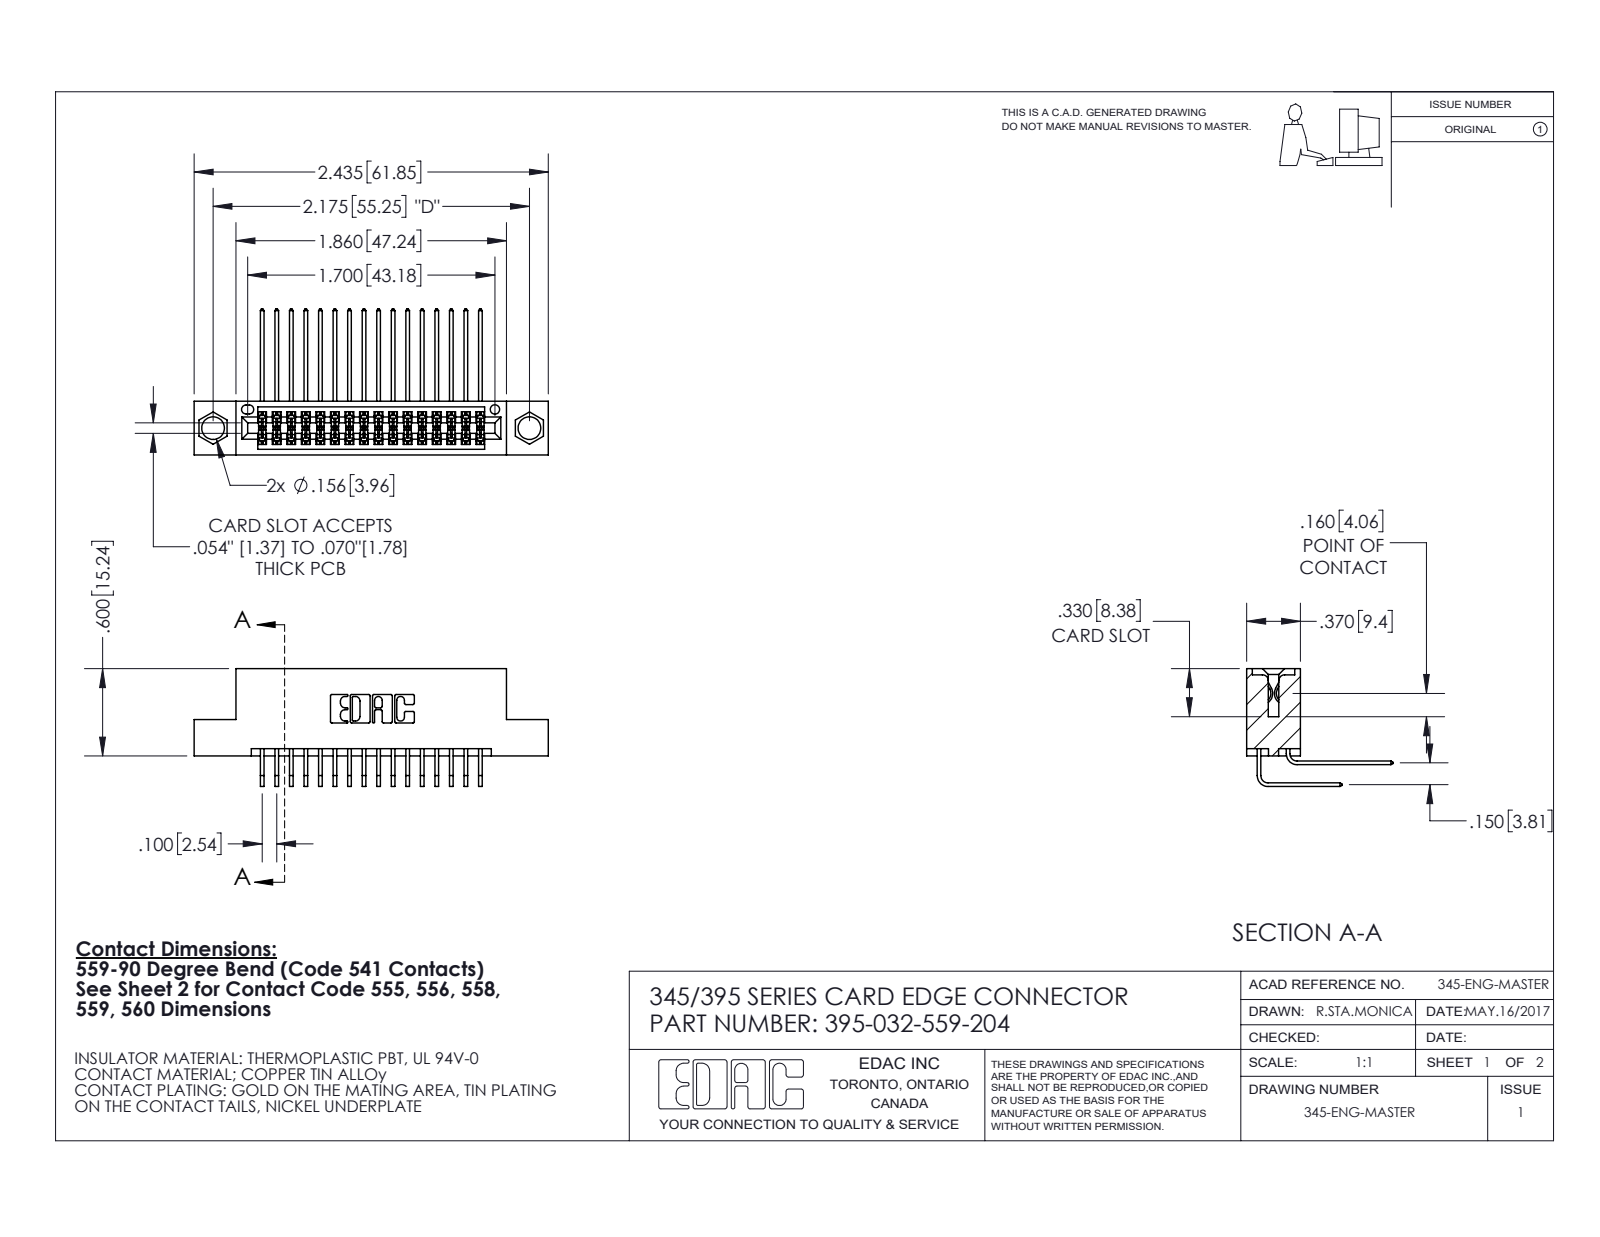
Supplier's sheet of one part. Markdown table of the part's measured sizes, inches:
| quantity | value |
| --- | --- |
| part name | 395-032-559-204; 345-292-001_559 Tail - 2; 345 Part_Flush Mounting Lugs - 0.156 Dia-TI; 345-292-001_558 559 Tail - 1 |
| STEP written by | SolidWorks 2020 (CONFIG_CONTROL_DESIGN) |
| units | inches |
| bodies | 33 solids, 1804 faces (1214 planar, 590 cylindrical, 0 other) |
| overall size | 2.435 × 1.005 × 0.809 |
| volume | 0.357 in³ |
| surface area | 13.73 in² |
| round holes (diameter × count) | 0.156 × 2, 0.064 × 1 |
| partial cylindrical surfaces (radius × count) | 0.006 × 64, 0.01 × 22, 0.007 × 6, 0.031 × 6, 0.026 × 3, 0.014 × 2, 0.019 × 2, 0.022 × 2 |
| main face-to-face distances | 0.072, 0.298, 0.2, 0.37, 0.098, 0.272, 0.025, 0.225, 0.15, 0.175 |
| hole center spacings | 0.27, 1.942, 2.175 |
